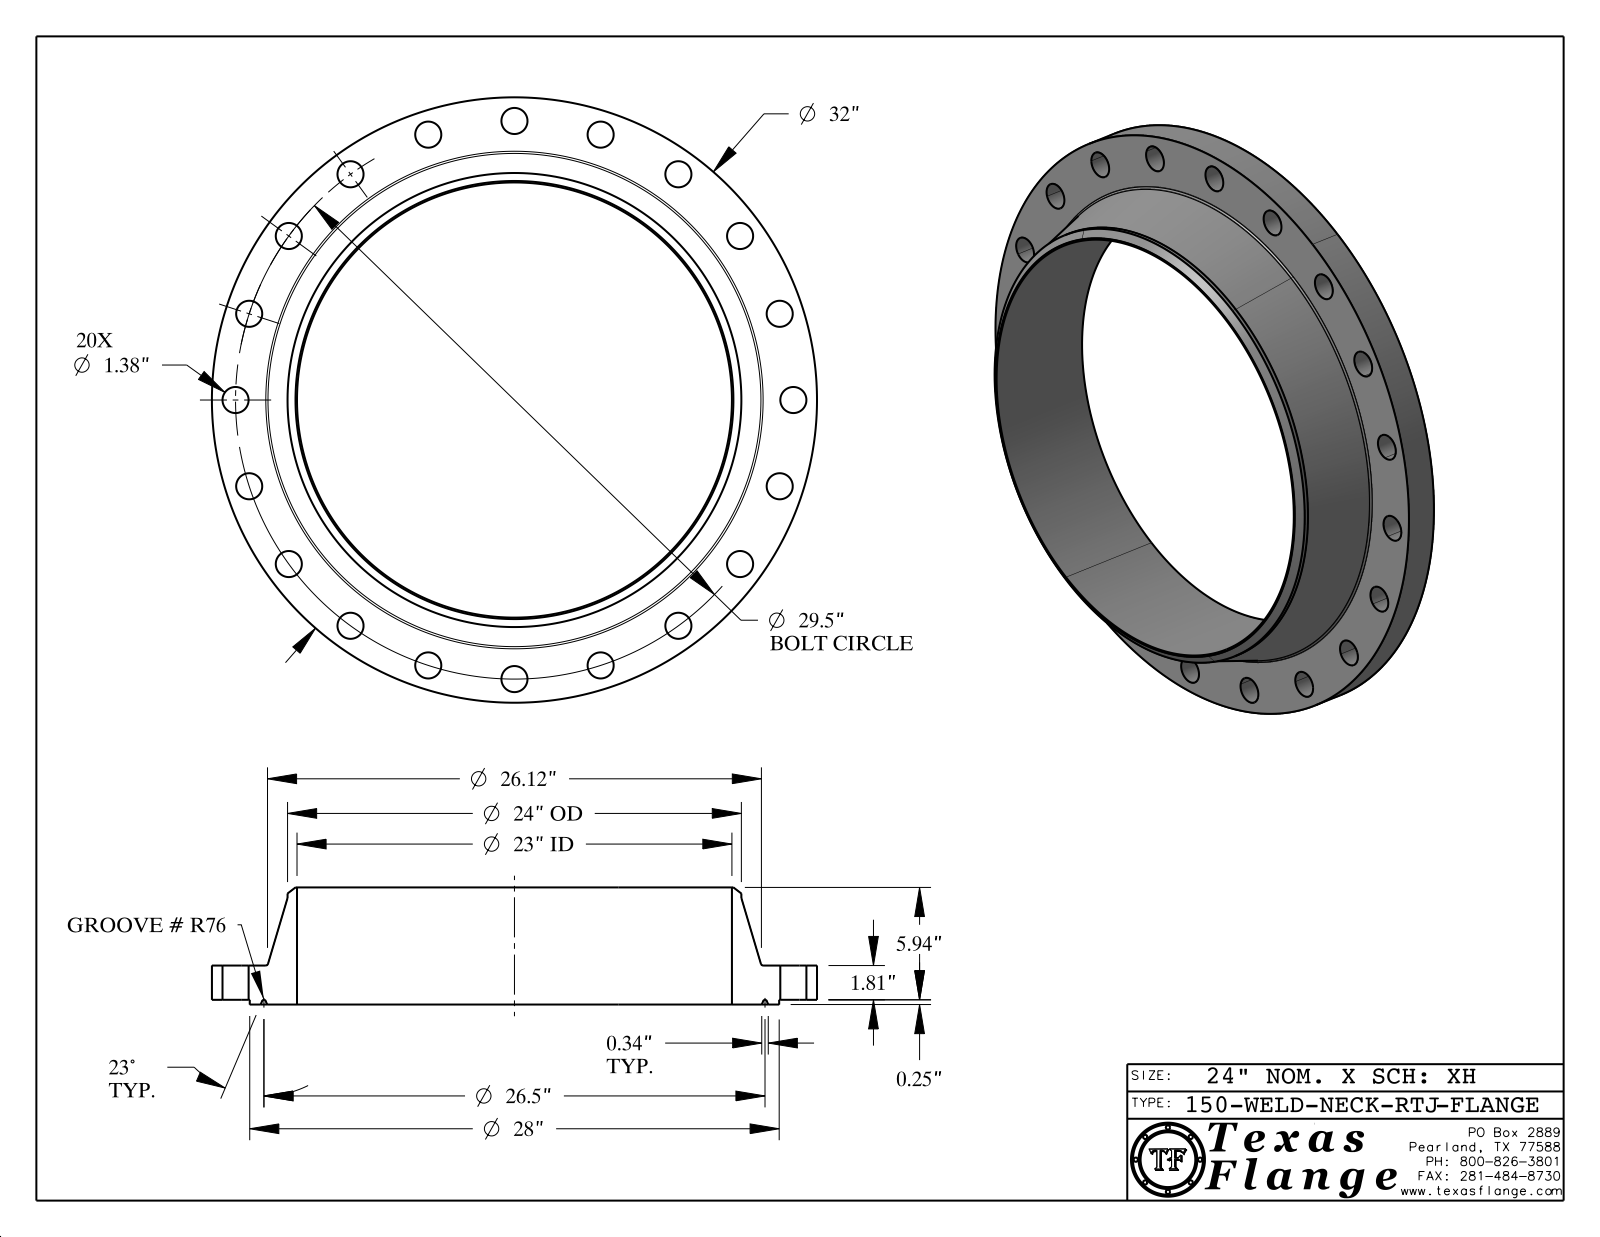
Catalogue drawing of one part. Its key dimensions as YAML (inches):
part_name: "150-WELD-NECK-RTJ"
step_written_by: "CATIA V5 STEP AP214 (AUTOMOTIVE_DESIGN)"
units: inches
bodies: {solids: 1, faces: 453, planar: 371, cylindrical: 68, other: 14}
overall_size: [32, 32, 6.19]
volume: 989.1
surface_area: 1786
round_holes:
  - {diameter: 1.38, count: 20}
  - {diameter: 0.495, count: 1}
  - {diameter: 23, count: 1}
round_bosses_or_shafts:
  - {diameter: 0.03, count: 8}
  - {diameter: 32, count: 1}
  - {diameter: 28, count: 1}
  - {diameter: 24, count: 1}
  - {diameter: 0.39, count: 1}
face_to_face_distances: [2.06, 0.25, 1.81, 6.19, 5.94, 4.13, 2.055, 1.805, 4.135, 0.148]
hole_center_spacings: [14.75, 29.137, 4.615, 17.34, 20.859, 23.866, 26.285, 9.116]
